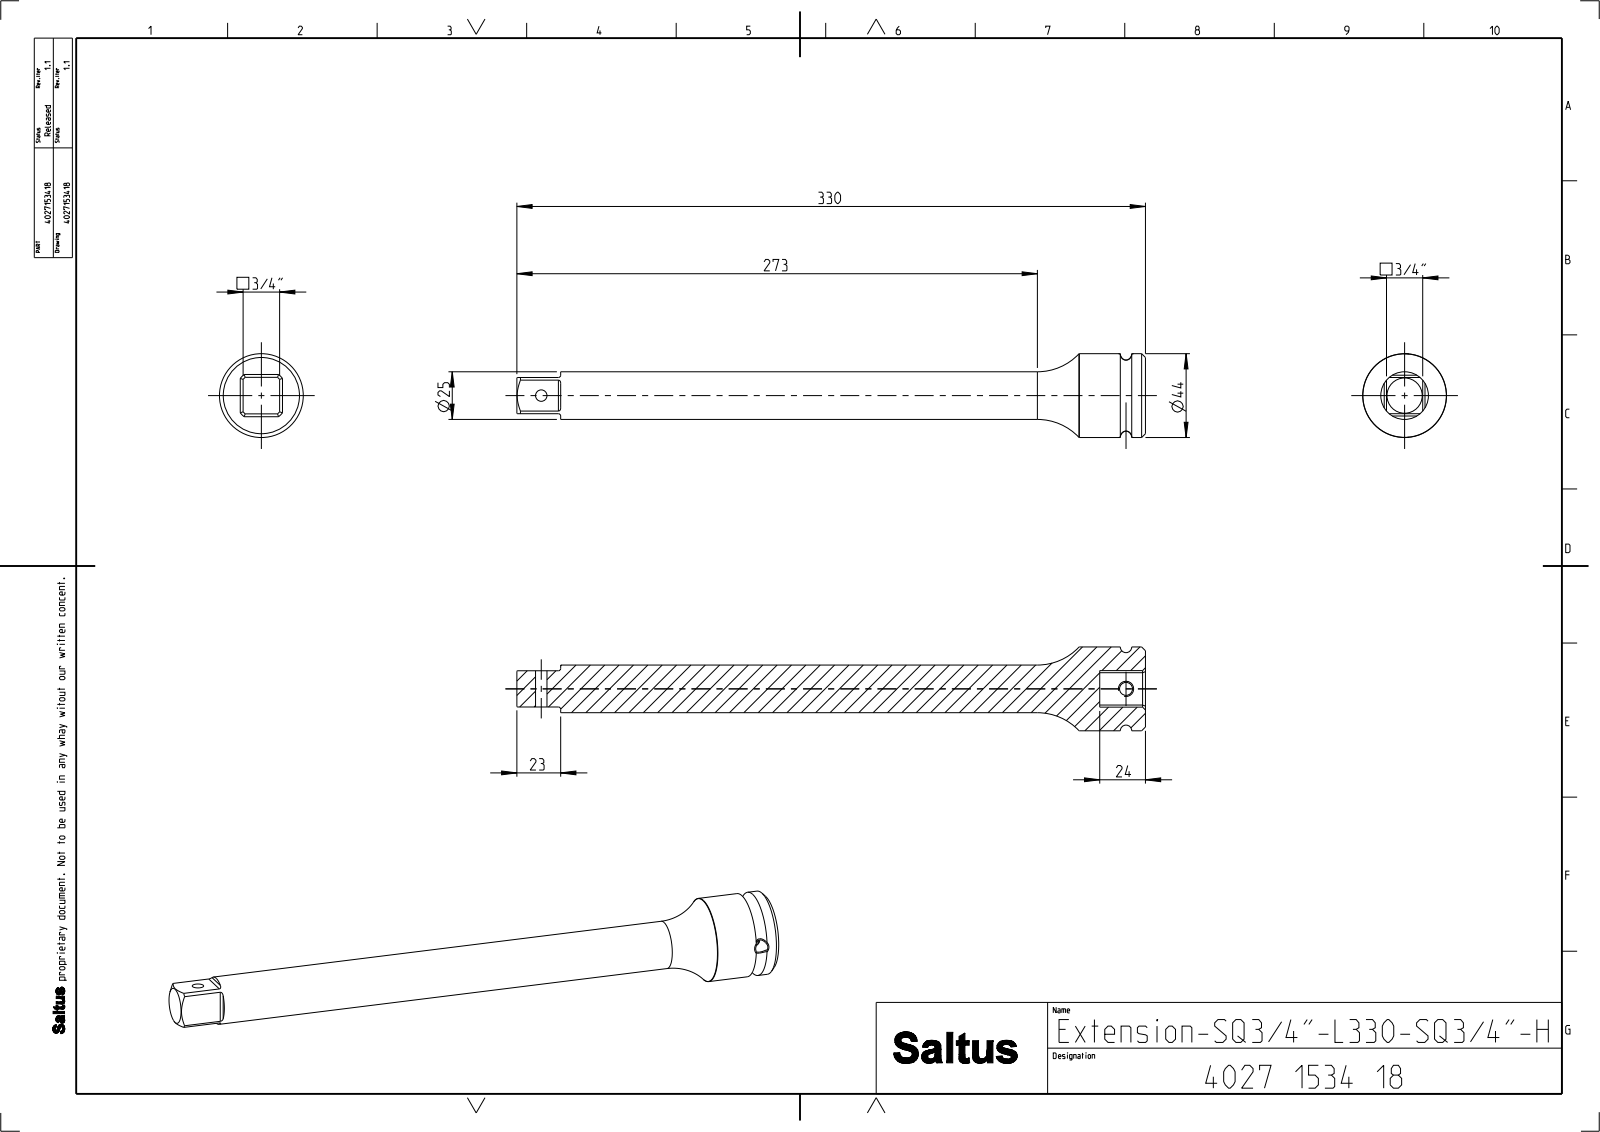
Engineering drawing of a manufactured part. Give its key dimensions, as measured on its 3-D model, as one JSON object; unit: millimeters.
{"part_name": "4027153418", "step_written_by": "CREO PARAMETRIC BY PTC INC, 2022414 (CONFIG_CONTROL_DESIGN)", "units": "millimeters", "bodies": {"solids": 1, "faces": 57, "planar": 19, "cylindrical": 24, "other": 14}, "overall_size": [330, 44, 44], "volume_mm3": 188681, "surface_area_mm2": 33550, "round_holes": [[6, 1], [6.8, 1], [8, 1]], "round_bosses_or_shafts": [[44, 1], [25, 1]], "partial_cylinders_radius": [[1.2, 4], [12.8, 1]], "face_to_face_distances": [19.09, 19.18, 19, 24, 330, 306, 307, 283, 23]}
